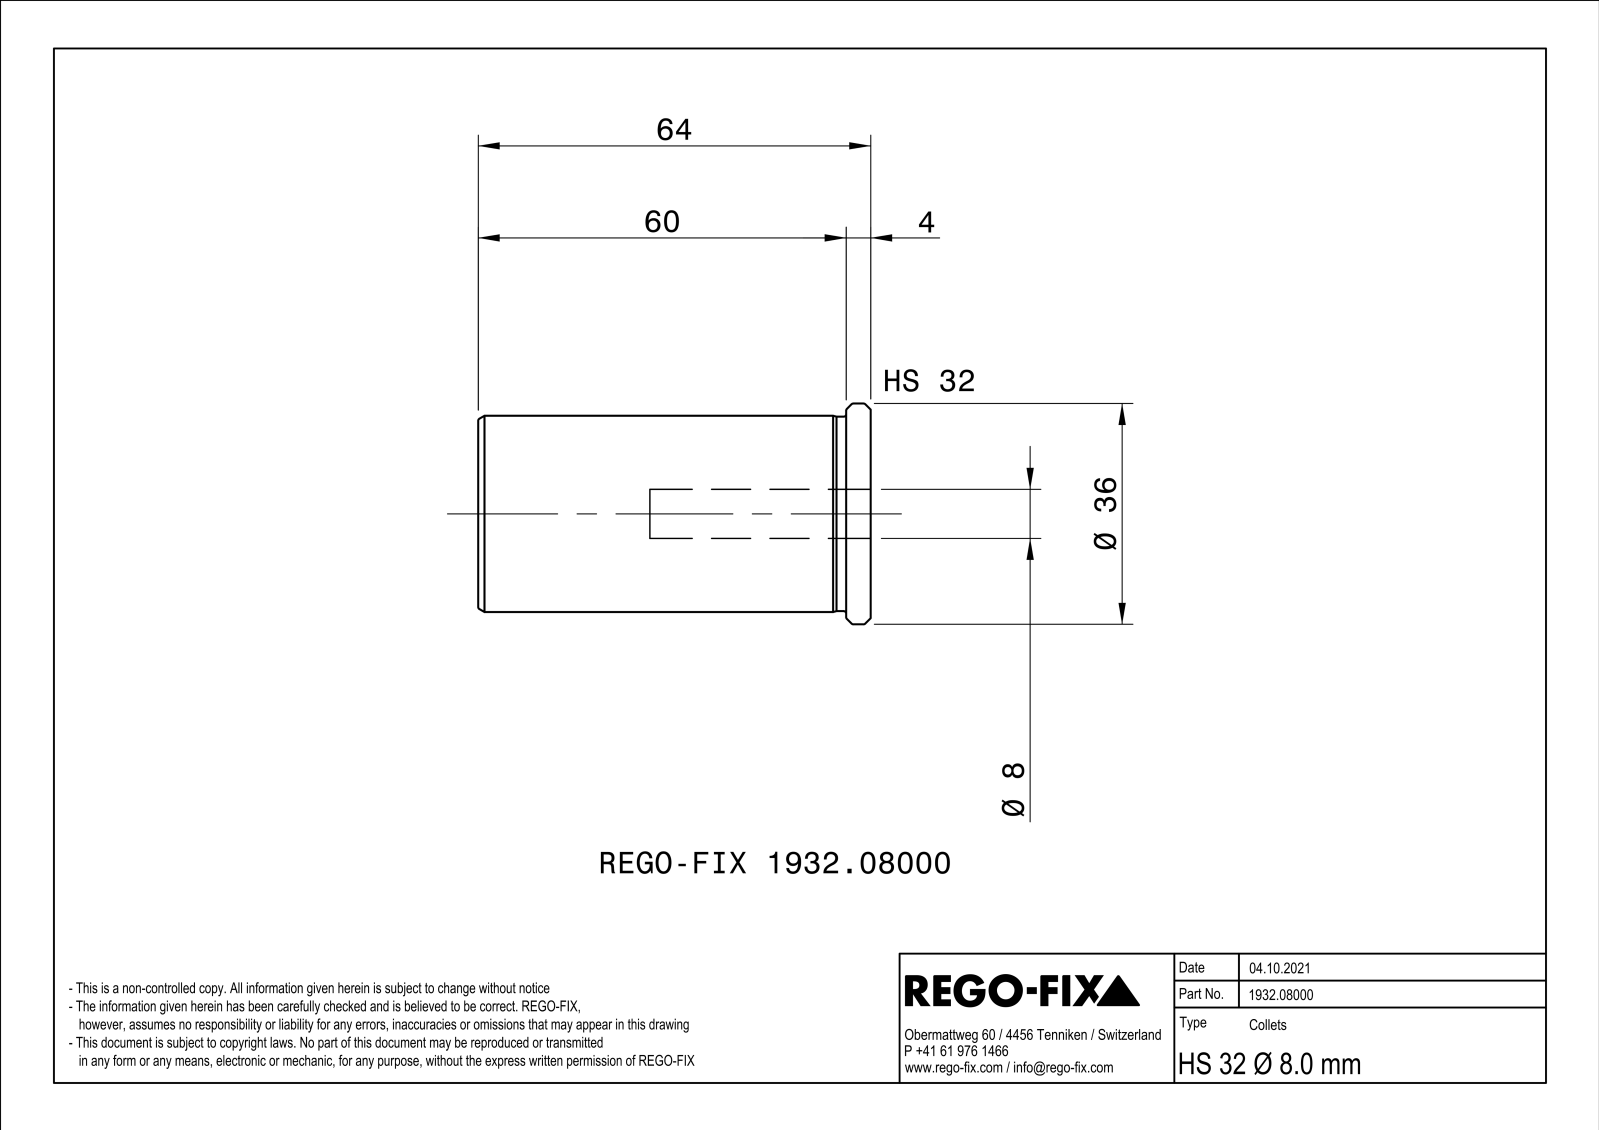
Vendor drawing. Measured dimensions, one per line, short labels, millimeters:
name: NOCUT
written by: SIEMENS PLM Software Solid Edge ST10 (AUTOMOTIVE_DESIGN)
unit: mm
bodies: 1 solid, 73 faces (22 planar, 12 cylindrical, 39 other)
size: 64 × 35.99 × 35.99
volume: 39 158 mm³; area: 13 774 mm²
holes: 1× ⌀8, 1× ⌀10, 1× ⌀26.5
bosses: 1× ⌀36, 1× ⌀32, 1× ⌀31.7
face distances: 1, 64, 4, 60
